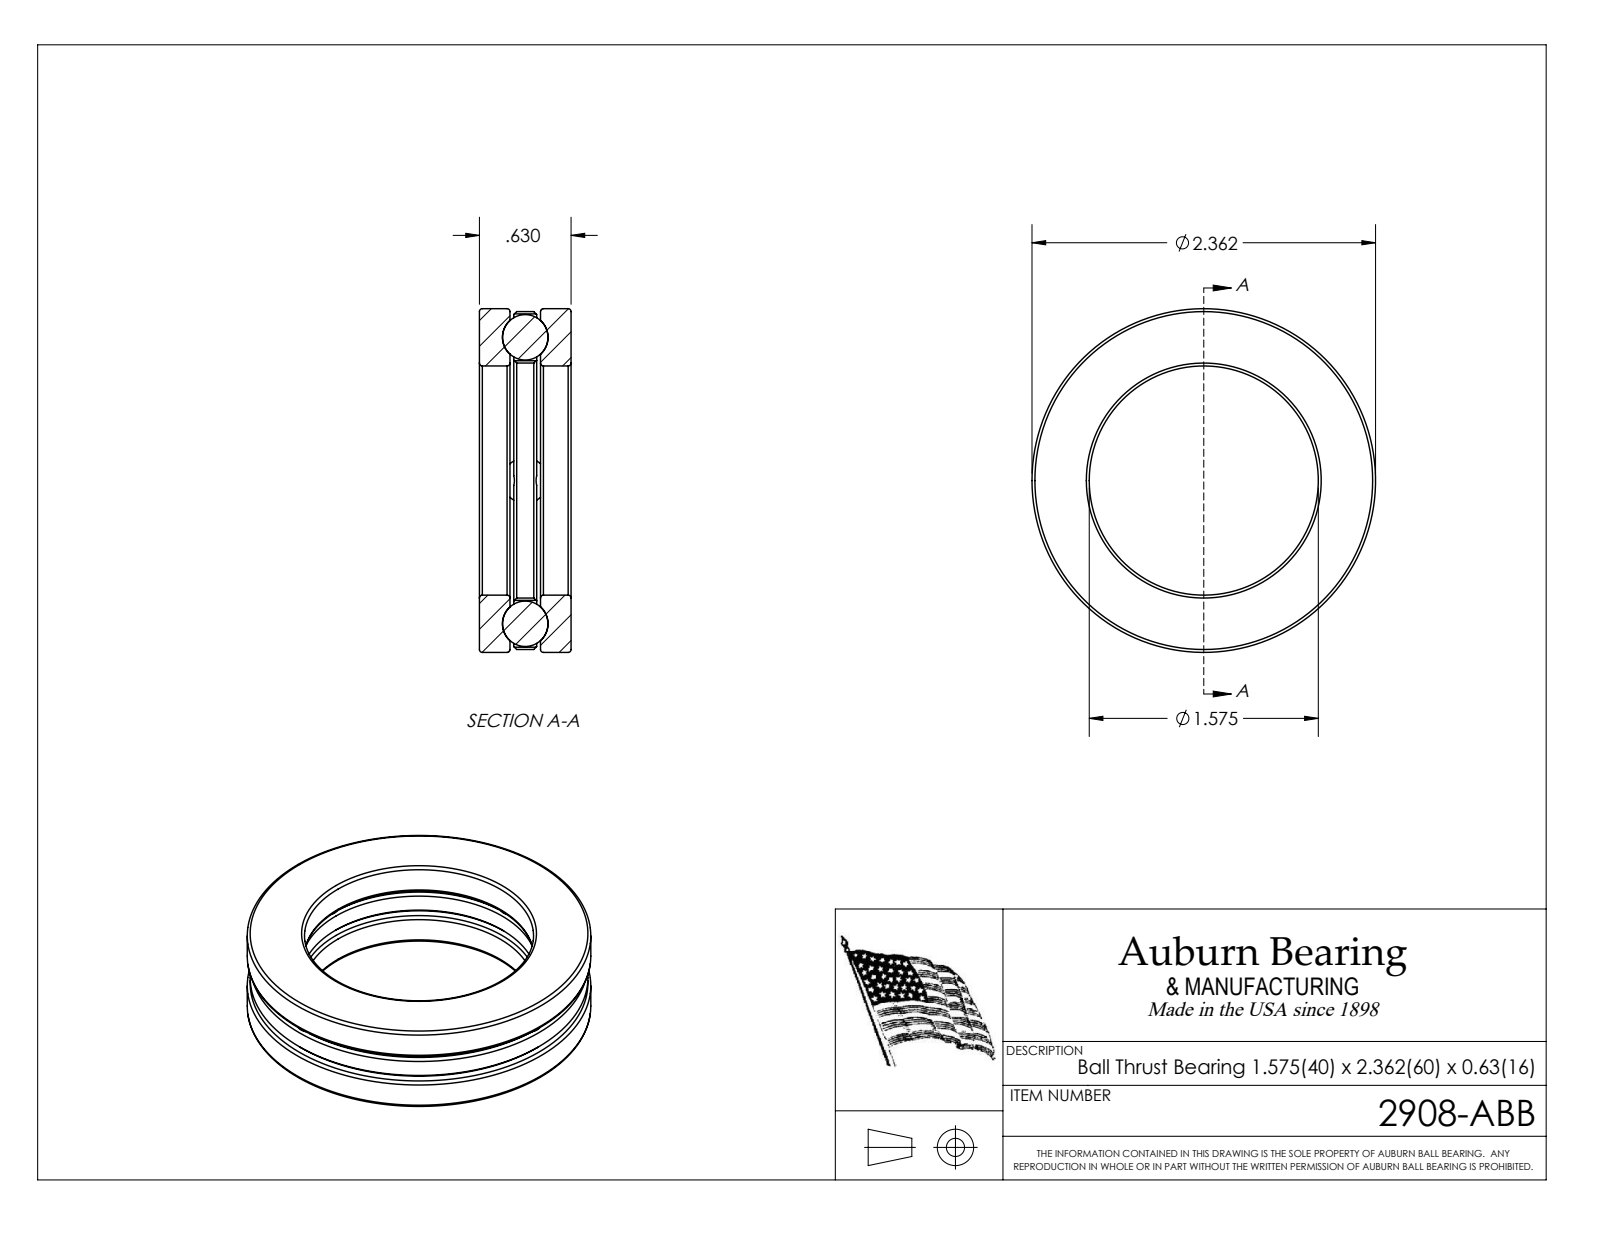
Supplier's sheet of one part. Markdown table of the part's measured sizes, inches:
| quantity | value |
| --- | --- |
| part name | 2908-ABB |
| STEP written by | SolidWorks 2017 (CONFIG_CONTROL_DESIGN) |
| units | inches |
| bodies | 7 solids, 42 faces (14 planar, 10 cylindrical, 18 other) |
| overall size | 2.362 × 2.362 × 0.63 |
| volume | 1.269 in³ |
| surface area | 22.1 in² |
| round holes (diameter × count) | 0.322 × 4, 1.575 × 1, 1.615 × 1 |
| round bosses / shafts (diameter × count) | 2.362 × 1, 2.322 × 1 |
| main face-to-face distances | 0.236, 0.394, 0.63, 0.157, 0.21, 0.42, 0.026, 0.184, 0.21 |
| hole center spacings | 0.984, 1.392, 1.969 |
